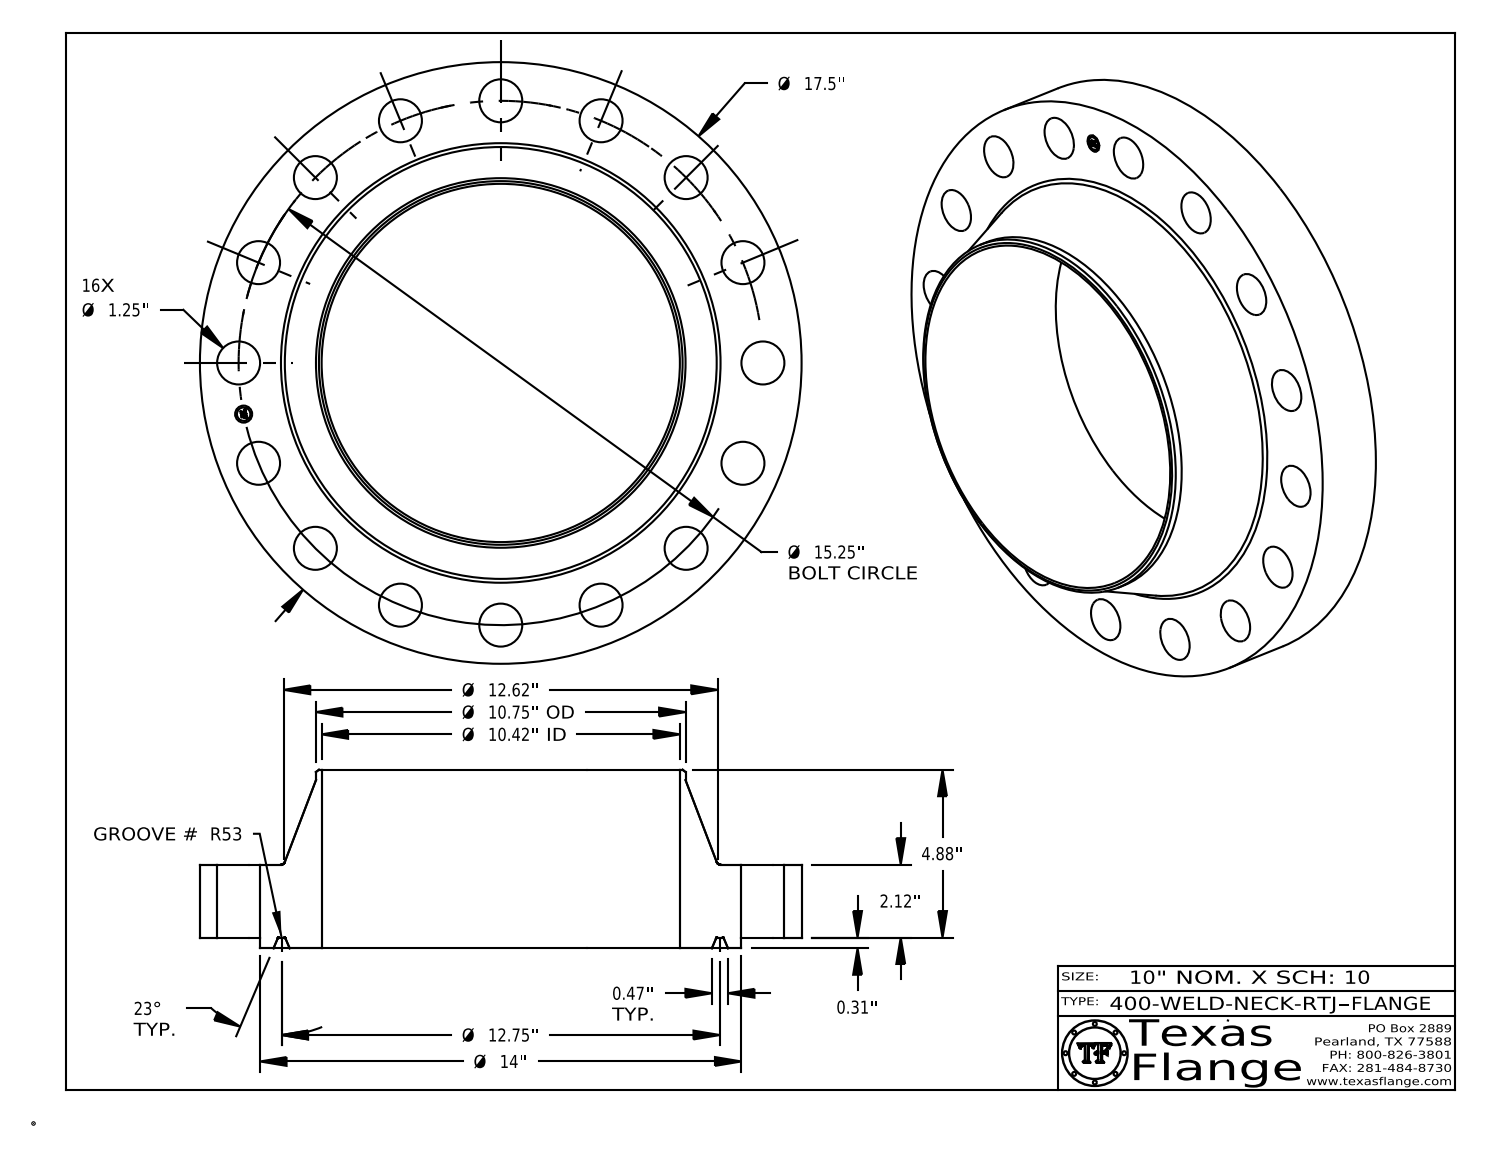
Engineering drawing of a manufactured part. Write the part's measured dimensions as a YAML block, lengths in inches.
part_name: "400-WELD-NECK-RTJ"
step_written_by: "CATIA V5 STEP AP214 (AUTOMOTIVE_DESIGN)"
units: inches
bodies: {solids: 1, faces: 445, planar: 371, cylindrical: 60, other: 14}
overall_size: [17.5, 17.5, 5.193]
volume: 360.9
surface_area: 791.2
round_holes:
  - {diameter: 1.25, count: 16}
  - {diameter: 0.495, count: 1}
  - {diameter: 10.42, count: 1}
round_bosses_or_shafts:
  - {diameter: 0.03, count: 8}
  - {diameter: 17.5, count: 1}
  - {diameter: 14, count: 1}
  - {diameter: 10.75, count: 1}
  - {diameter: 0.39, count: 1}
face_to_face_distances: [2.12, 0.313, 2.433, 5.193, 4.88, 2.76, 0.015, 2.418, 2.105, 2.775]
hole_center_spacings: [8.472, 10.783, 14.957, 14.089, 7.625, 2.975, 2.975, 5.836]
